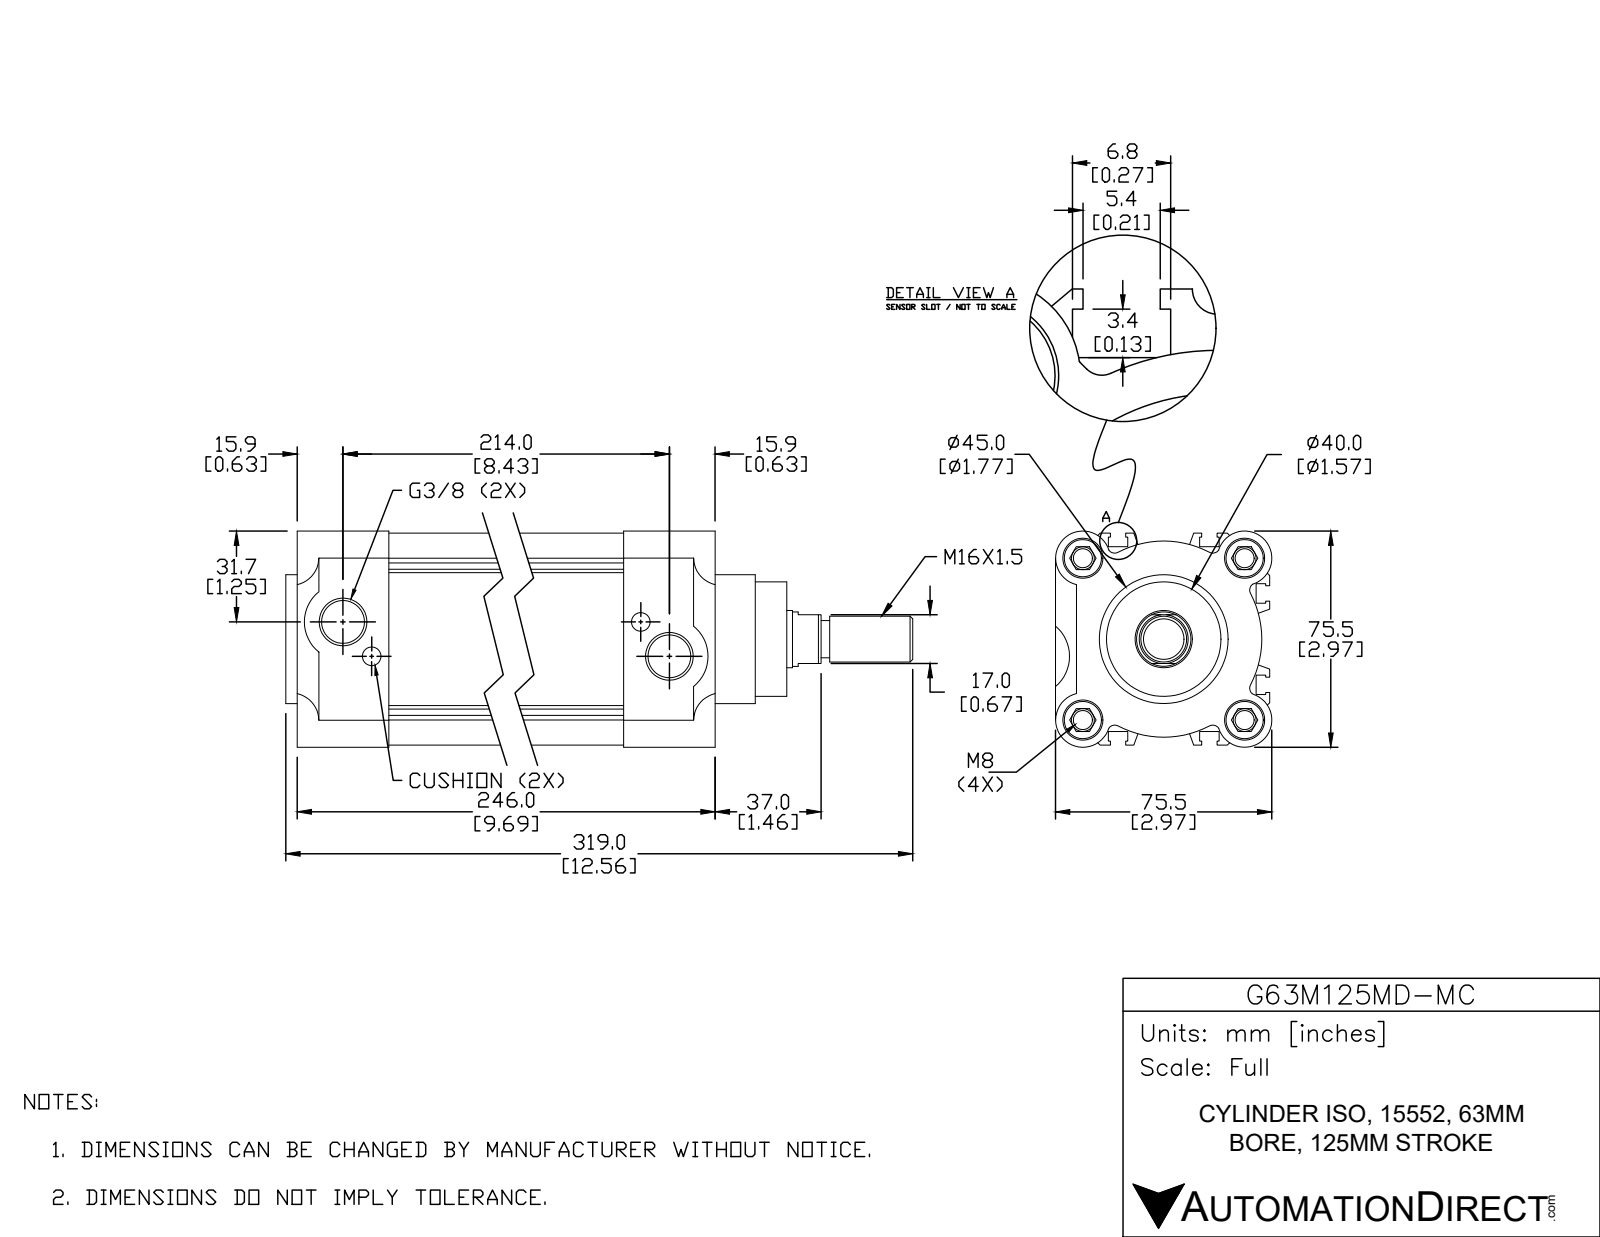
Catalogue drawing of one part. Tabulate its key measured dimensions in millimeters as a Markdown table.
| quantity | value |
| --- | --- |
| part name | 63121-HR; G63M125MD-MC; 63121125-R; 63-HL (+1 more) |
| STEP written by | SolidWorks 2015 (CONFIG_CONTROL_DESIGN) |
| units | millimeters |
| bodies | 4 solids, 422 faces (240 planar, 138 cylindrical, 44 other) |
| overall size | 319 × 75.5 × 75.5 |
| volume | 899 600 mm³ |
| surface area | 209 000 mm² |
| round holes (diameter × count) | 6.7 × 4, 14 × 4, 6.5 × 2, 6.7 × 2, 15 × 2, 20 × 1 |
| round bosses / shafts (diameter × count) | 13 × 5, 63 × 1, 45 × 1, 40 × 1, 19 × 1, 16 × 1 |
| partial cylindrical surfaces (radius × count) | 0.1 × 6, 2.5 × 6, 8.7 × 4, 9.5 × 4, 13.5 × 2, 34 × 1, 34.2 × 1 |
| main face-to-face distances | 4.7, 9, 173, 69.2, 32, 41, 205, 214, 31.9, 49.2 |
| hole center spacings | 40, 56.5, 15.6, 79.9, 204, 194.4, 214.4 |
